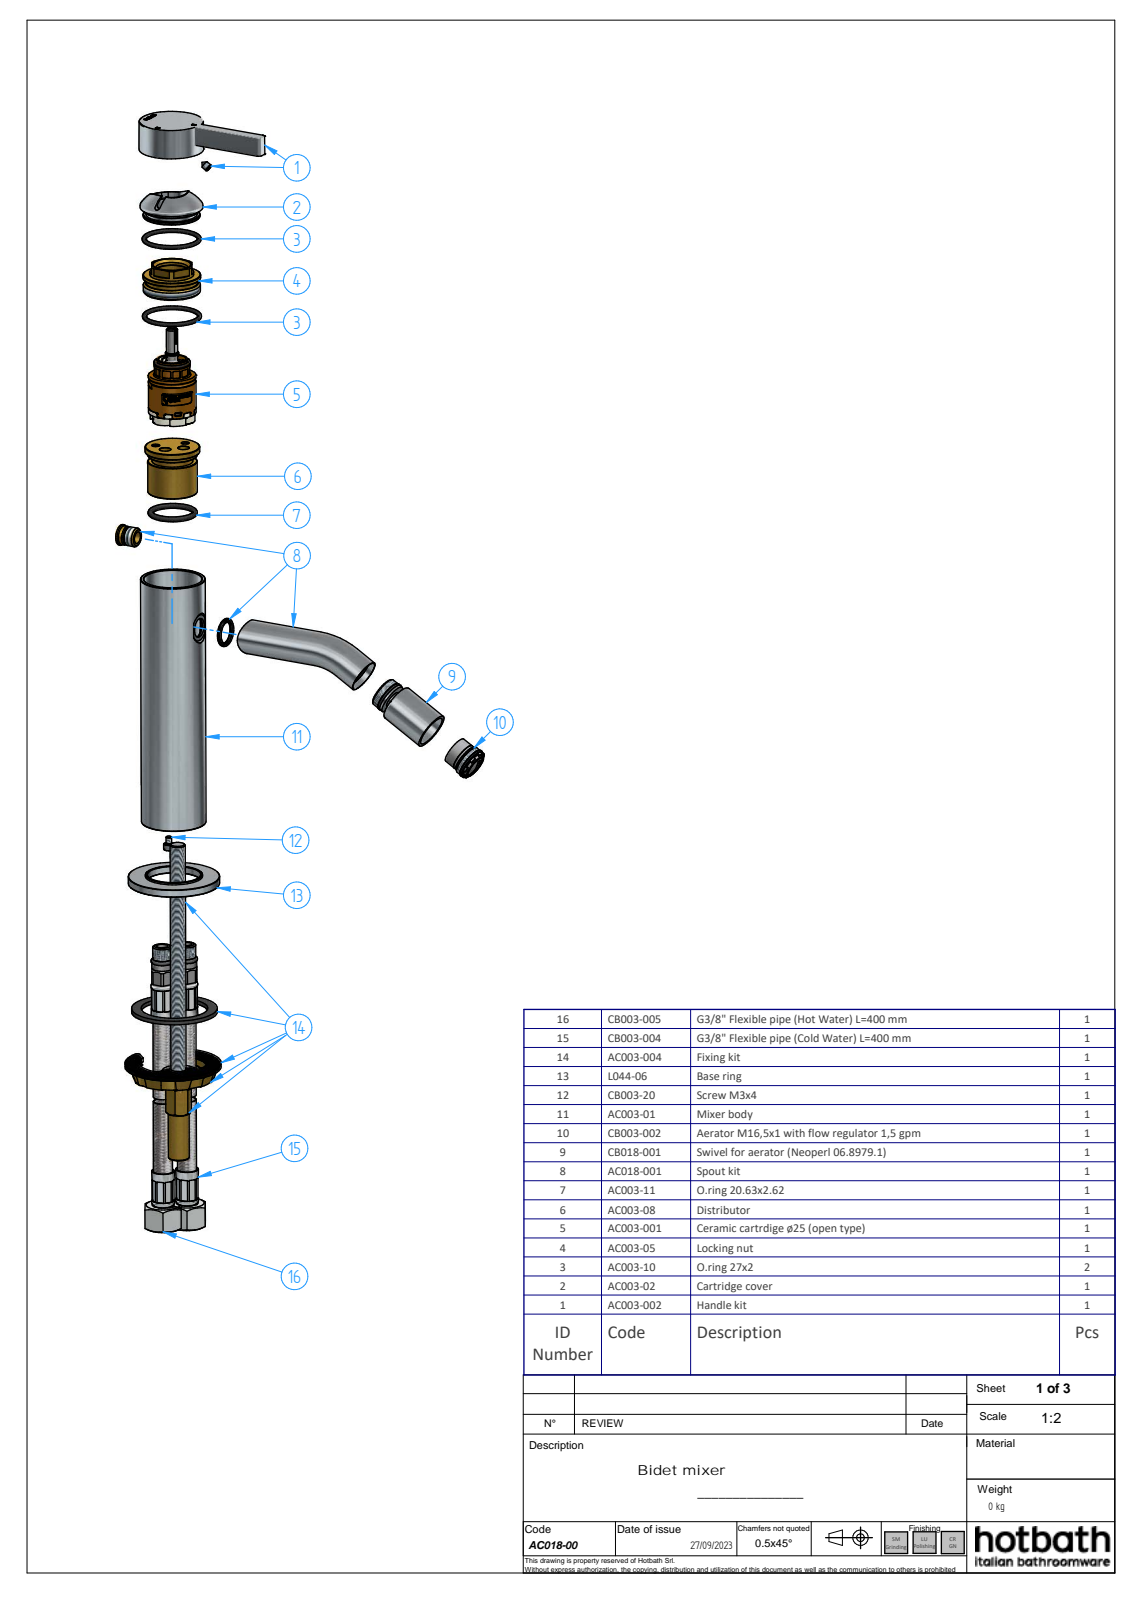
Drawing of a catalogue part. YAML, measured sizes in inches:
part_name: "AC018-00; L044-06; AC003-01; AC003-02 (+8 more)"
step_written_by: "Solid Edge (AUTOMOTIVE_DESIGN)"
units: inches
bodies: {solids: 9, faces: 426, planar: 168, cylindrical: 79, other: 179}
overall_size: [6.122, 5.468, 1.89]
volume: 3.413
surface_area: 83.28
round_holes:
  - {diameter: 0.394, count: 2}
  - {diameter: 0.543, count: 2}
  - {diameter: 0.128, count: 1}
  - {diameter: 0.157, count: 1}
  - {diameter: 0.236, count: 1}
  - {diameter: 0.48, count: 1}
  - {diameter: 0.548, count: 1}
  - {diameter: 0.574, count: 1}
  - {diameter: 0.607, count: 1}
  - {diameter: 0.644, count: 1}
  - {diameter: 0.659, count: 1}
  - {diameter: 0.669, count: 1}
round_bosses_or_shafts:
  - {diameter: 0.709, count: 2}
  - {diameter: 0.65, count: 2}
  - {diameter: 1.89, count: 1}
  - {diameter: 1.299, count: 1}
  - {diameter: 1.181, count: 1}
  - {diameter: 1.063, count: 1}
  - {diameter: 0.787, count: 1}
  - {diameter: 0.6, count: 1}
partial_cylinders:
  - {radius: 0.012, count: 6}
  - {radius: 0.02, count: 6}
  - {radius: 0.315, count: 3}
  - {radius: 0.022, count: 2}
  - {radius: 0.029, count: 2}
  - {radius: 0.079, count: 2}
  - {radius: 0.787, count: 2}
  - {radius: 0.019, count: 1}
face_to_face_distances: [5.965, 0.11, 6.075, 0.394, 0.689, 5.386, 5.276, 0.157, 0.295, 0.059]
